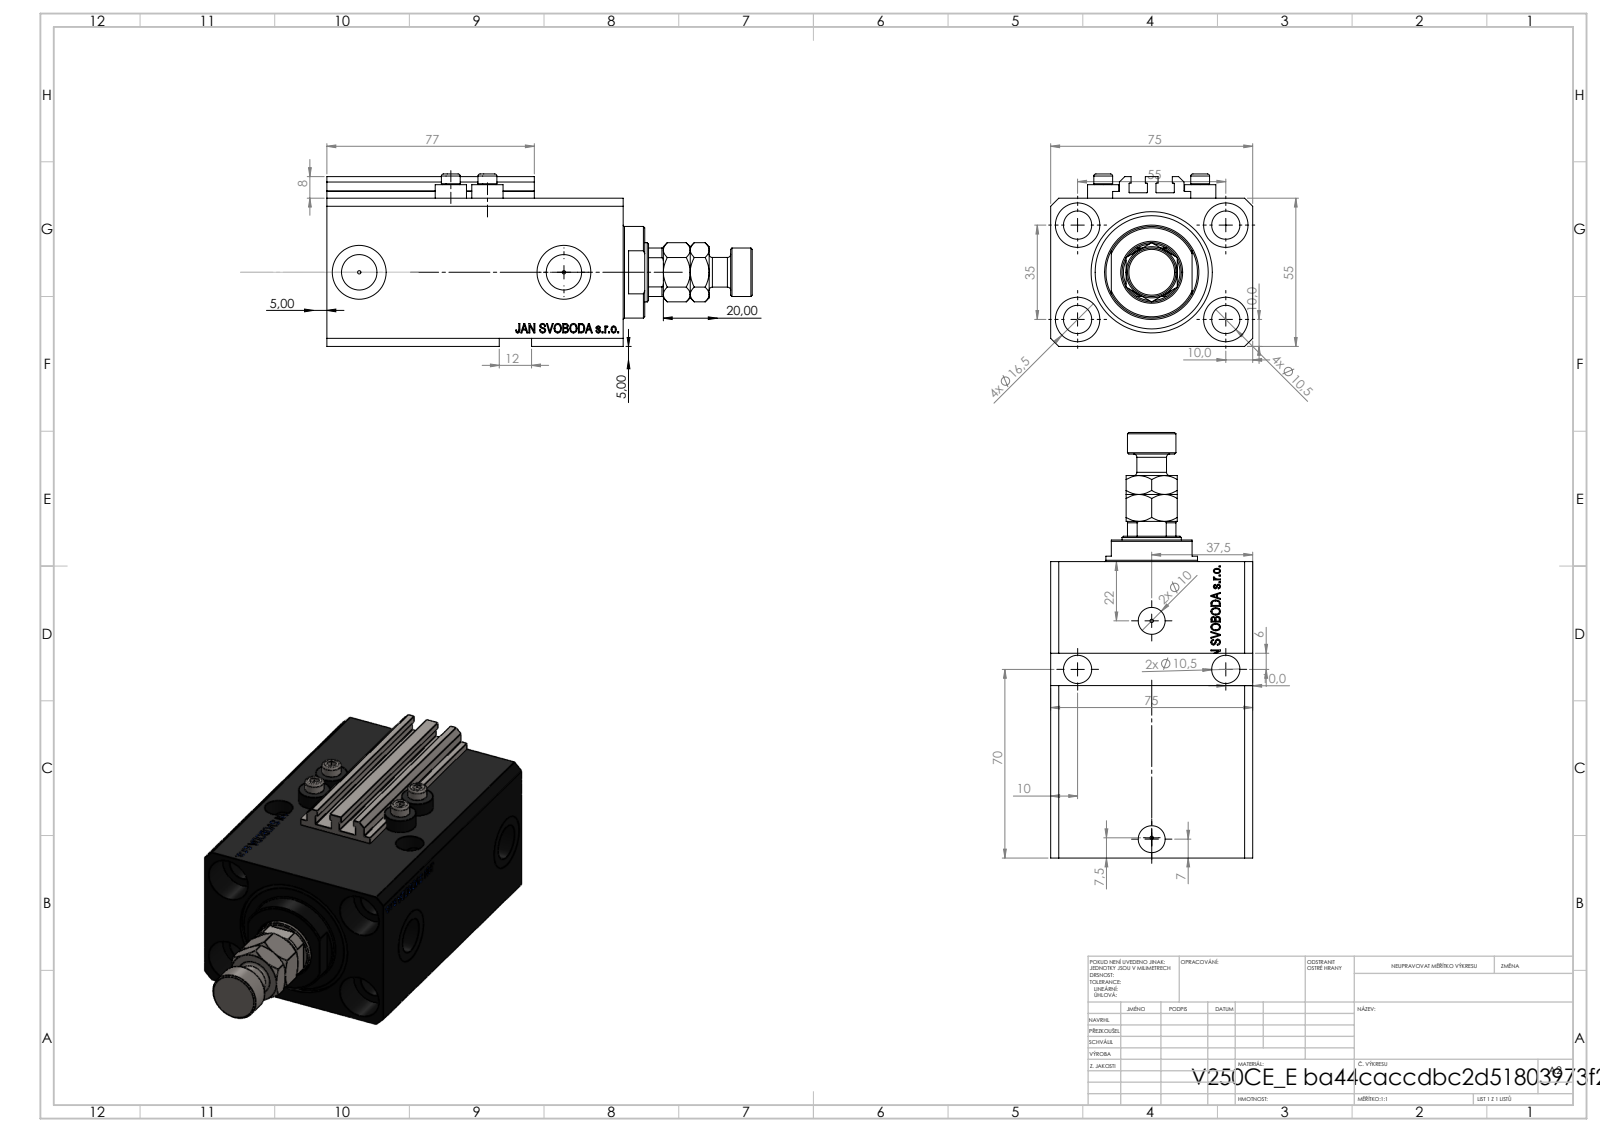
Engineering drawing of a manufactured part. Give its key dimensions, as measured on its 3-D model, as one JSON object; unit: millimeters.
{"part_name": "V250CE_VC_E; V250CE_C_VCP; MFA; V250CE_E_Body (+1 more)", "step_written_by": "SolidWorks 2019 (CONFIG_CONTROL_DESIGN)", "units": "millimeters", "bodies": {"solids": 9, "faces": 1152, "planar": 534, "cylindrical": 162, "other": 456}, "overall_size": [158, 75, 64], "volume_mm3": 385785, "surface_area_mm2": 99488, "round_holes": [[10.5, 9], [1.25, 4], [4, 4], [16.5, 4], [10, 2], [13.16, 2], [20, 2], [22, 1], [32, 1], [45, 1]], "round_bosses_or_shafts": [[11.6, 4], [7, 4], [34, 1], [18, 1], [11, 1]], "partial_cylinders_radius": [[0.2, 10], [10.5, 1]], "face_to_face_distances": [55, 75, 15, 110, 95, 9.9, 3, 85.1, 100.1, 2.5], "hole_center_spacings": [32.6, 32.87, 55, 68.74, 13.6, 14.09, 23.05, 25.81]}
